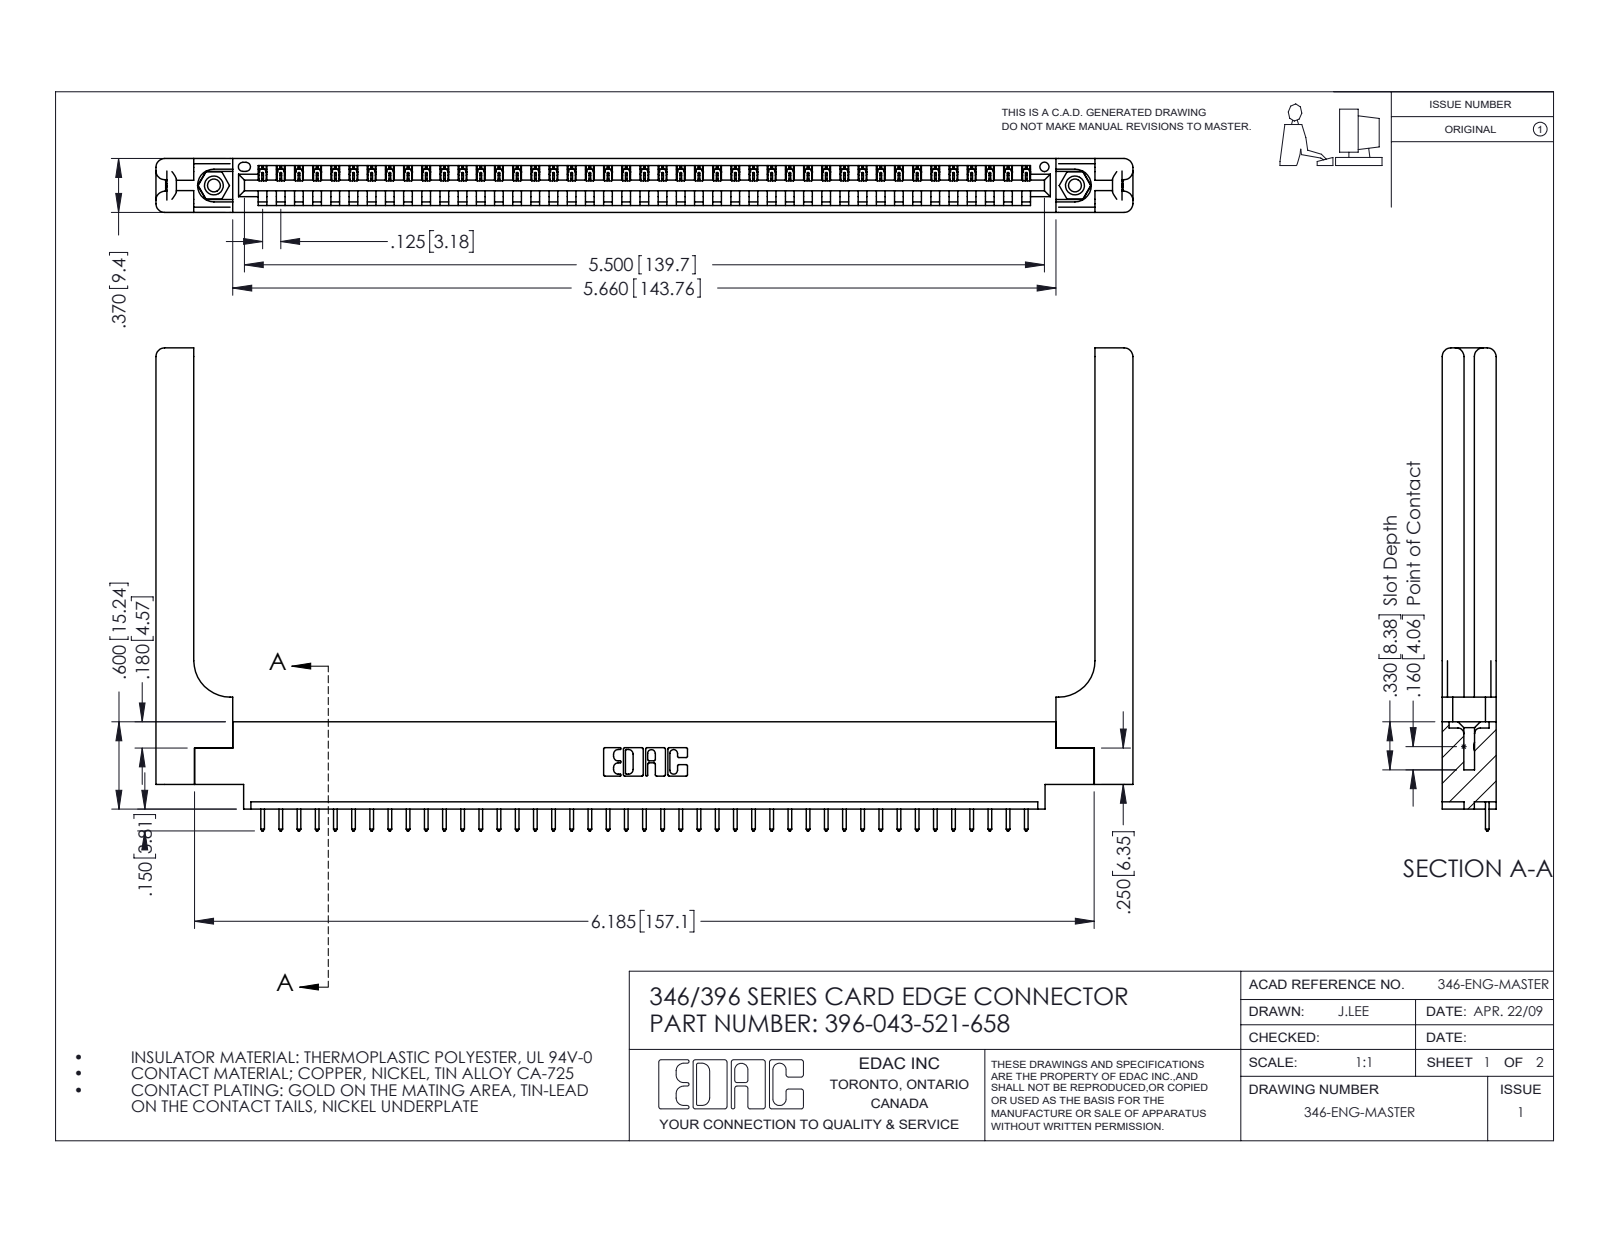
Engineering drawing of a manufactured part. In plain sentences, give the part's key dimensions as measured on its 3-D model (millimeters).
The part is named "346-220-058_345-220-058; 346 Part_0.170 Offset - 0.156 Dia-TH; 396-043-521-658; 345-250-001_345-250-001-102 (+1 more)". Its 3-D file was written by "SolidWorks 2016 (CONFIG_CONTROL_DESIGN)". It is 48 solids with 2876 faces: 1948 planar, 868 cylindrical and 60 other. Overall it measures 170.6 by 84.3 by 9.4 millimeters. Its volume is 23 580 cubic millimeters and its surface area 24 920 square millimeters. Round holes: 2 of diameter 2.3, 2 of diameter 3.2, 2 of diameter 4, 1 of diameter 1.6. Round bosses or shafts: 2 of diameter 3.9. Partial cylindrical surfaces (rounded edges, fillets, slot ends): 86 of radius 0.2, 86 of radius 0.3, 22 of radius 0.3, 16 of radius 1.5, 6 of radius 0.2, 6 of radius 0.8, 3 of radius 0.7, 2 of radius 0.8. The main face-to-face distances are 9.4, 1.2, 8.2, 1.8, 3.8, 3.8, 6.4, 7.6, 0.6, 5.6. The hole center spacings are 6.2, 145.1, 150.4.
